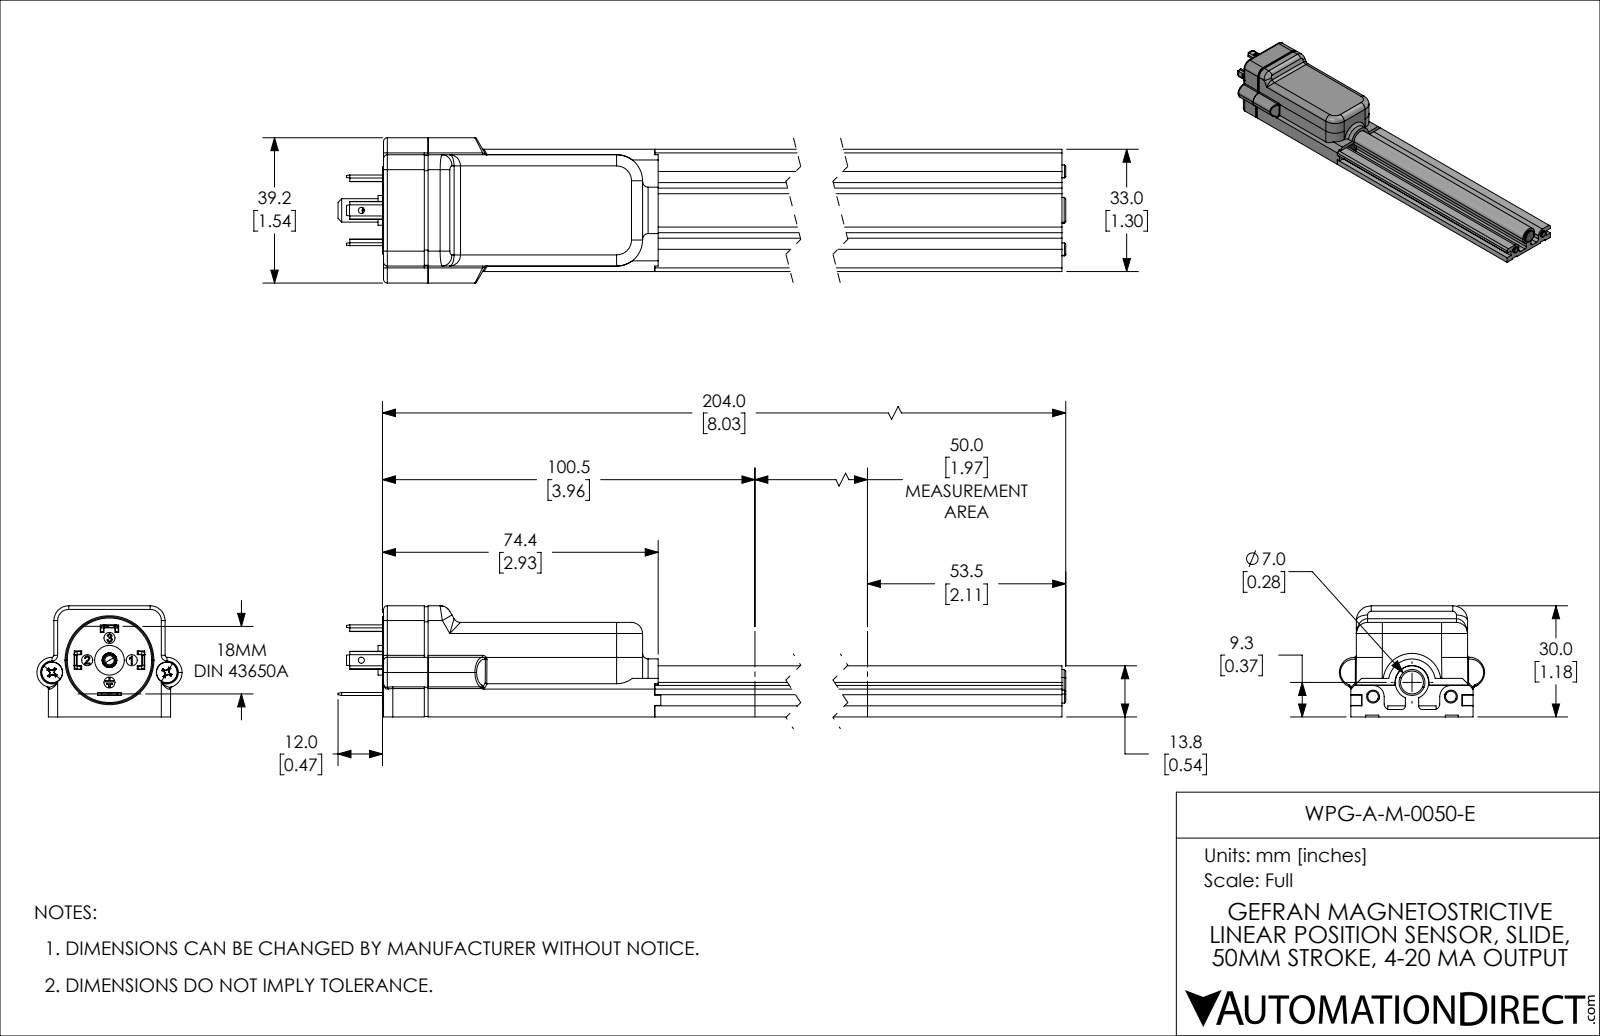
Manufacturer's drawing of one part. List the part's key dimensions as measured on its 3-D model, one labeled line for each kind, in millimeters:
Part name (STEP PRODUCT): WPG-A-M-0050-E
STEP written by: SolidWorks 2021 (CONFIG_CONTROL_DESIGN)
Units: millimetres
Bodies: 15 solids, 589 faces (371 planar, 139 cylindrical, 79 other)
Overall size (bounding box): 216 × 39.2 × 30
Volume: 90 128 mm³ · Surface area: 34 342 mm²
Round holes (diameter × count): ⌀3 ×5, ⌀1.5 ×2, ⌀1.65 ×2, ⌀3.2 ×2, ⌀5.7 ×2, ⌀1.6 ×1, ⌀2.5 ×1, ⌀4 ×1
Round bosses / shafts (diameter × count): ⌀5.6 ×2, ⌀3.5 ×2, ⌀2.85 ×2, ⌀9 ×1, ⌀8 ×1, ⌀7 ×1, ⌀5.3 ×1, ⌀3.94 ×1
Partial cylindrical surfaces — rounded edges, fillets, slot ends (radius × count): R0.5 ×8, R3 ×8, R0.85 ×6, R1 ×5, R0.8 ×4, R1.5 ×4, R4.1 ×4, R7 ×4
Main face-to-face distances: 1, 1.5, 3, 2.5, 5.5, 30, 6, 22.5, 8.5, 25.5
Hole centre spacings: 6, 8.49, 10.06, 12, 12.3, 15.73, 15.85, 18.08
